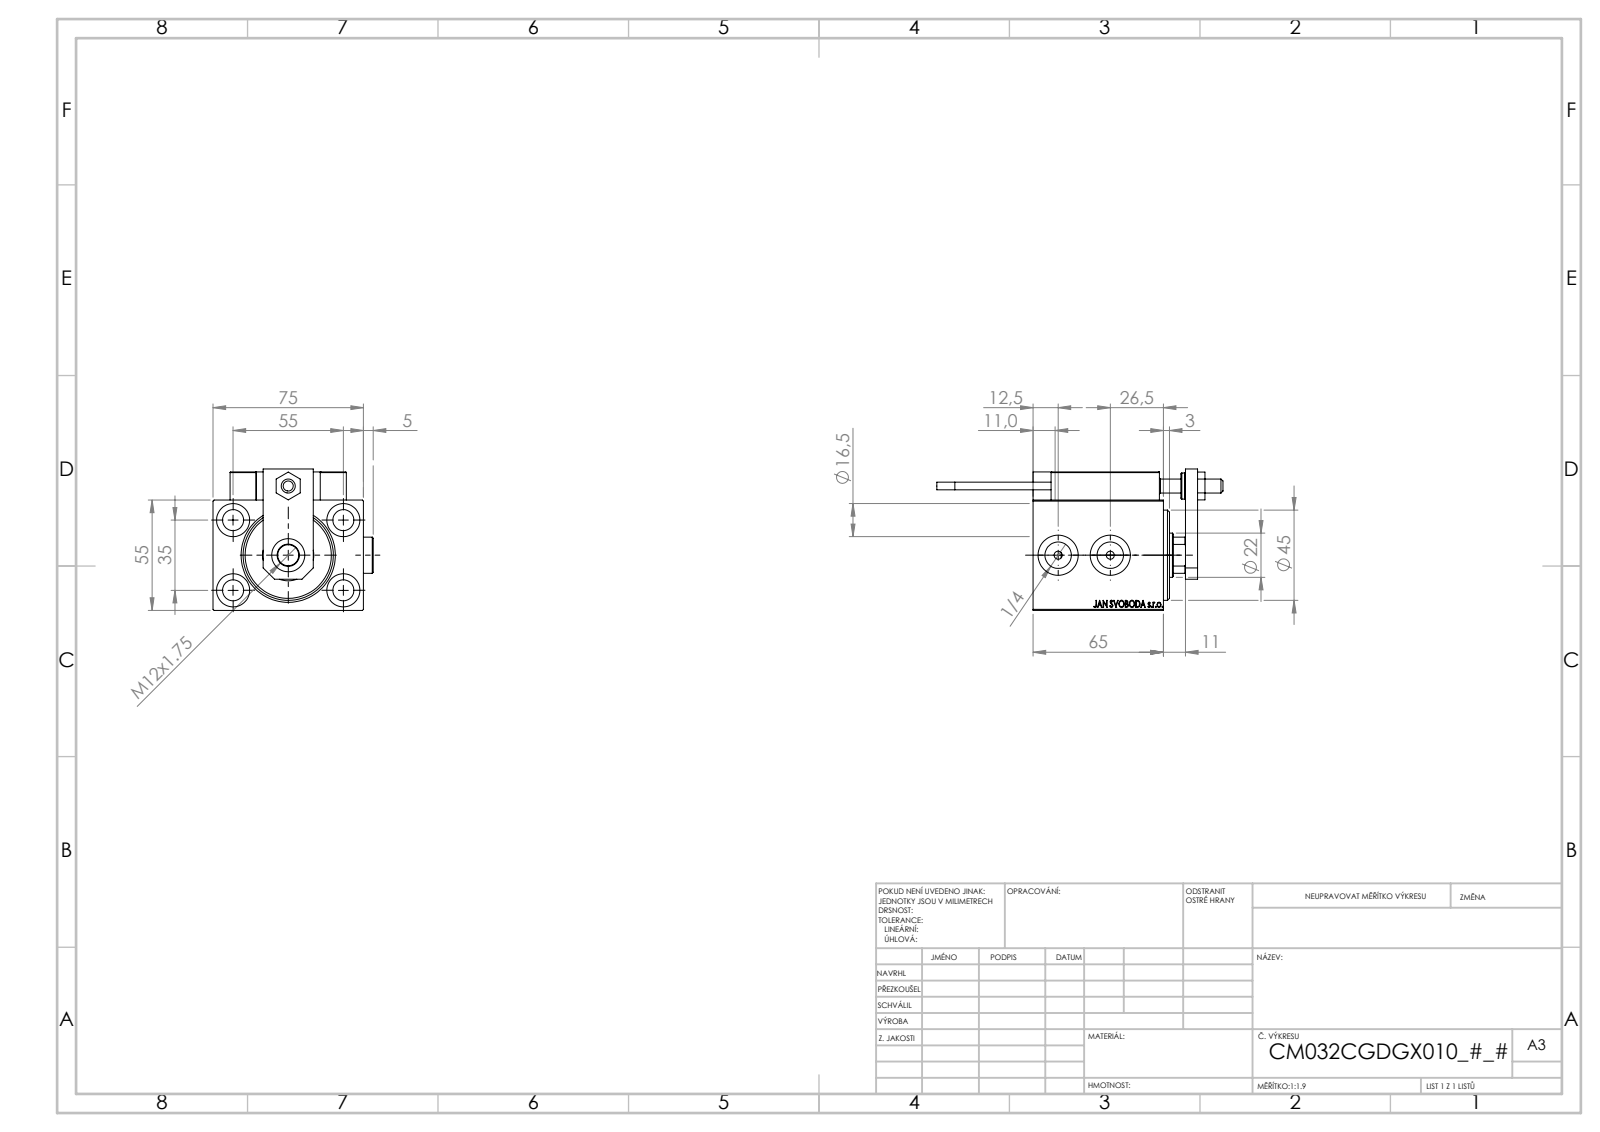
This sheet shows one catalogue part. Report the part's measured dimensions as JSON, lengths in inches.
{"part_name": "SWITCH X; Block; ALLEN BOLT D5; NUT_D12 (+7 more)", "step_written_by": "SolidWorks 2019 (CONFIG_CONTROL_DESIGN)", "units": "inches", "bodies": {"solids": 25, "faces": 1335, "planar": 595, "cylindrical": 202, "other": 538}, "overall_size": [5.618, 3.146, 2.776], "volume_in3": 16.9, "surface_area_in2": 127.7, "round_holes": [[0.157, 6], [0.315, 5], [0.413, 5], [0.65, 5], [0.126, 4], [0.197, 2], [0.518, 2], [0.787, 2], [0.276, 1], [0.866, 1], [1.004, 1], [1.26, 1]], "round_bosses_or_shafts": [[0.709, 2], [0.197, 2], [0.15, 2], [0.512, 1], [0.433, 1]], "partial_cylinders_radius": [[0.012, 30], [0.118, 2], [0.413, 1]], "face_to_face_distances": [2.165, 0.551, 2.953, 0.433, 0.197, 0.118, 2.126, 2.559, 2.717, 2.677], "hole_center_spacings": [1.283, 0.448, 0.674, 0.787, 1.094, 1.165, 1.169, 1.272]}
